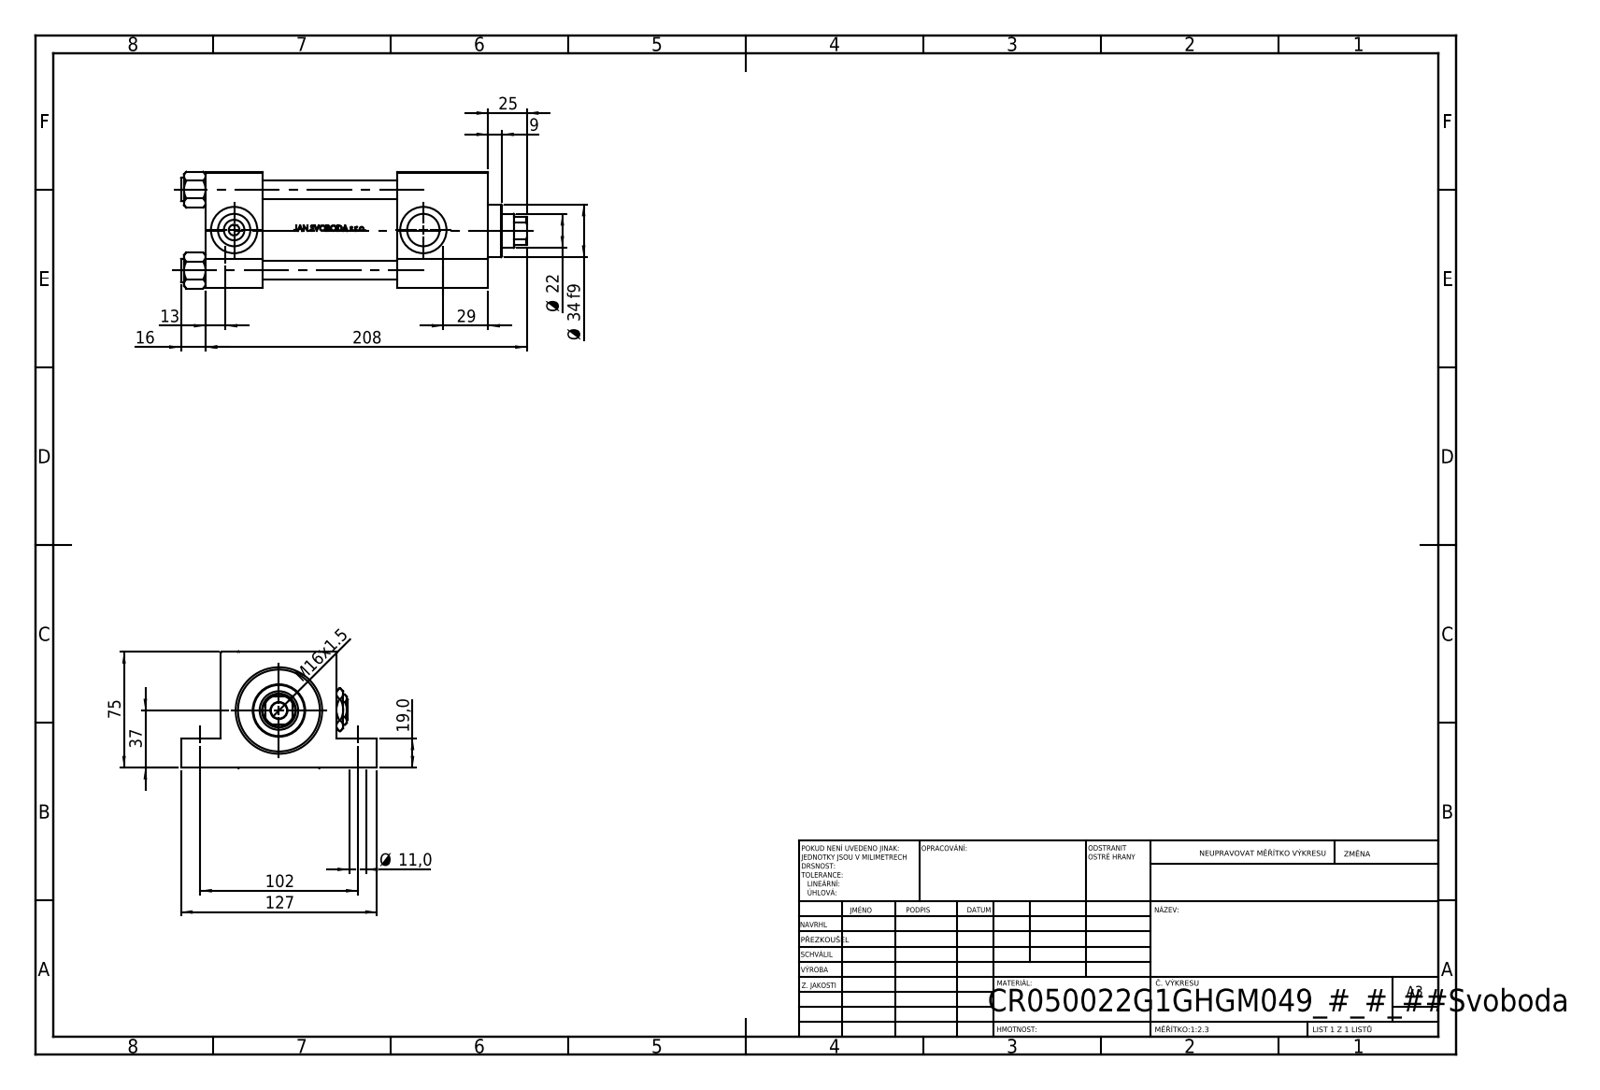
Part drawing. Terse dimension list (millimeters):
name: V215CR_G_TYCINKA; V215CR_G_Body; NUT_M5_G; V215CR_VCP_G (+2 more)
written by: SolidWorks 2019 (CONFIG_CONTROL_DESIGN)
unit: mm
bodies: 12 solids, 1134 faces (454 planar, 128 cylindrical, 552 other)
size: 224 × 127 × 75.54
volume: 791 032 mm³; area: 177 338 mm²
holes: 4× ⌀11, 4× ⌀12, 2× ⌀7, 2× ⌀20.96, 2× ⌀30, 1× ⌀10.5, 1× ⌀22, 1× ⌀25, 1× ⌀41, 1× ⌀50, 1× ⌀53
bosses: 4× ⌀15, 1× ⌀56, 1× ⌀34
rounds: 1× R10.5
face distances: 75, 37, 183, 146, 19, 56, 124, 87, 59, 26
hole spacings: 52.3, 36.63, 37.34, 73.96, 102, 141, 174.03, 122.5
